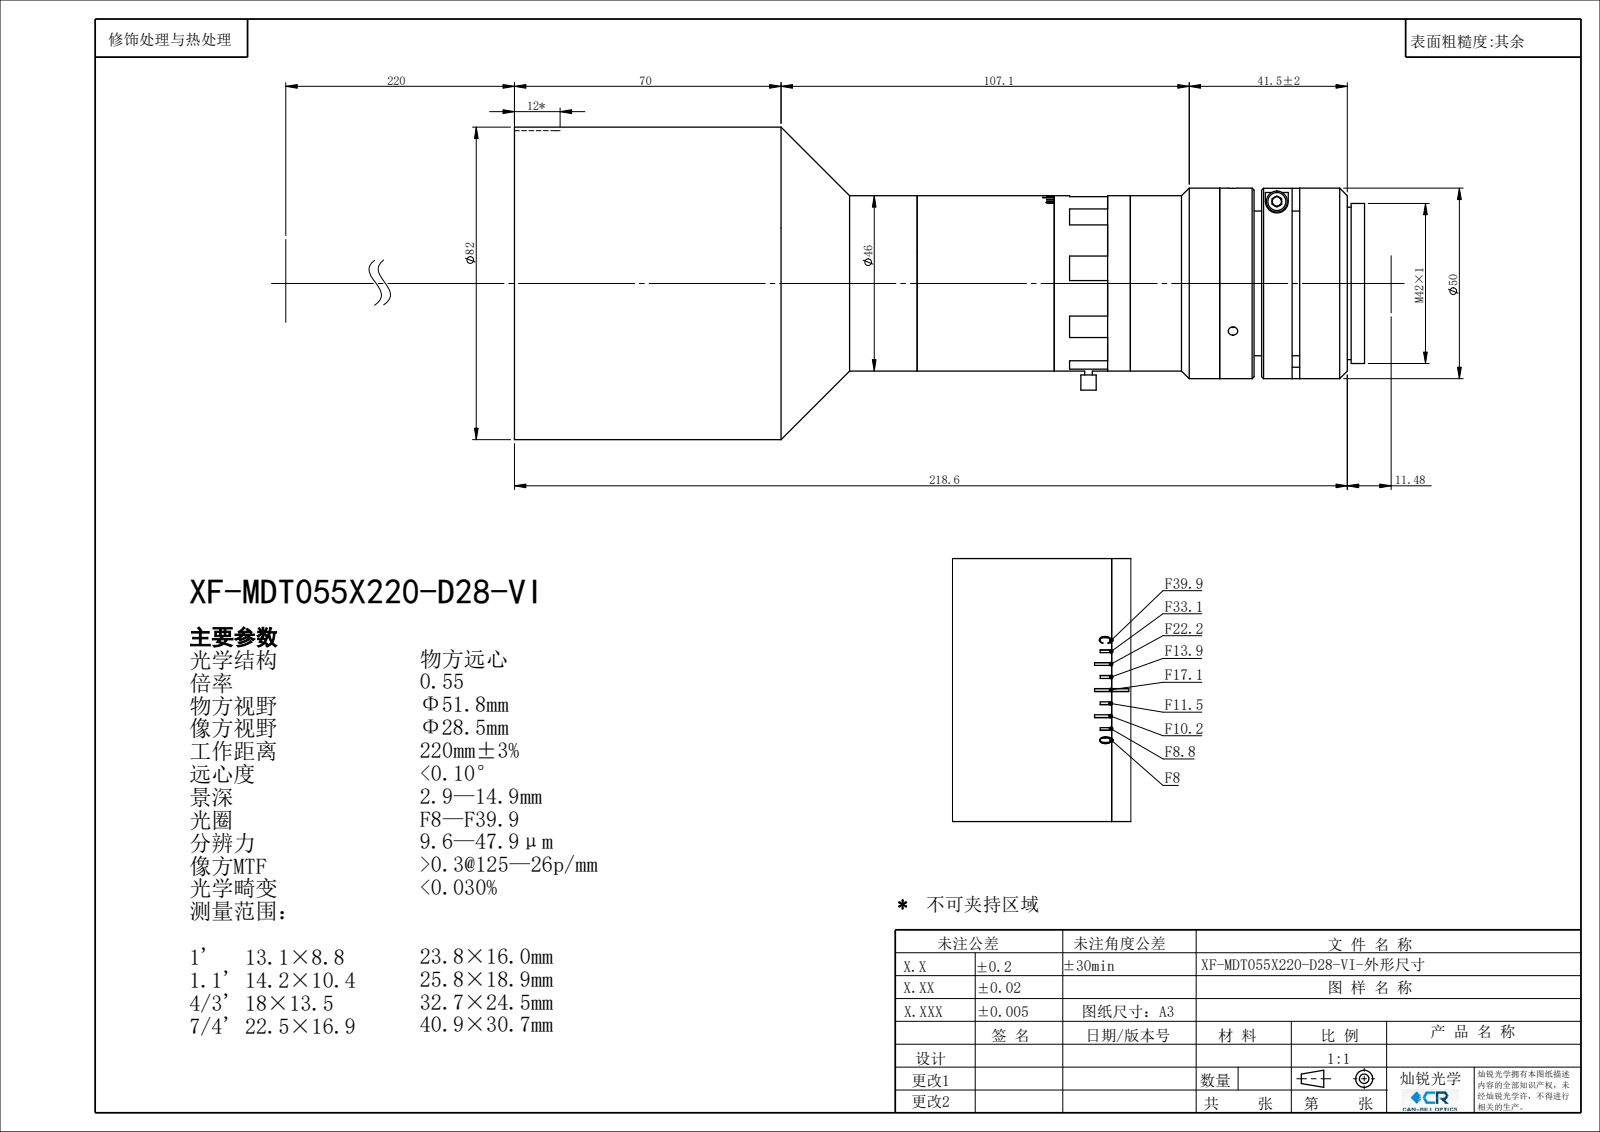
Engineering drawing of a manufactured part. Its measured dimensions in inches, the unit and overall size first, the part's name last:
Units: inches
Overall size (bounding box): 8.785 × 3.228 × 3.228
Round holes (diameter × count): ⌀0.098 ×3, ⌀1.26 ×1, ⌀1.378 ×1, ⌀1.496 ×1, ⌀2.756 ×1, ⌀2.992 ×1
Round bosses / shafts (diameter × count): ⌀3.228 ×1, ⌀1.969 ×1, ⌀1.811 ×1, ⌀1.654 ×1, ⌀1.575 ×1, ⌀0.217 ×1, ⌀0.157 ×1, ⌀0.118 ×1
Partial cylindrical surfaces — rounded edges, fillets, slot ends (radius × count): R0.787 ×9, R0.118 ×1, R0.902 ×1
Main face-to-face distances: 0.551, 0.079, 0.394, 7.154, 5.445, 1.709, 5.996, 1.158, 7.509, 2.064
Bodies: 0 solids, 141 faces (53 planar, 69 cylindrical, 19 other)
Part name (STEP PRODUCT): XF-MDT055X220-D28-VI
STEP written by: SolidWorks 2018 (CONFIG_CONTROL_DESIGN)
